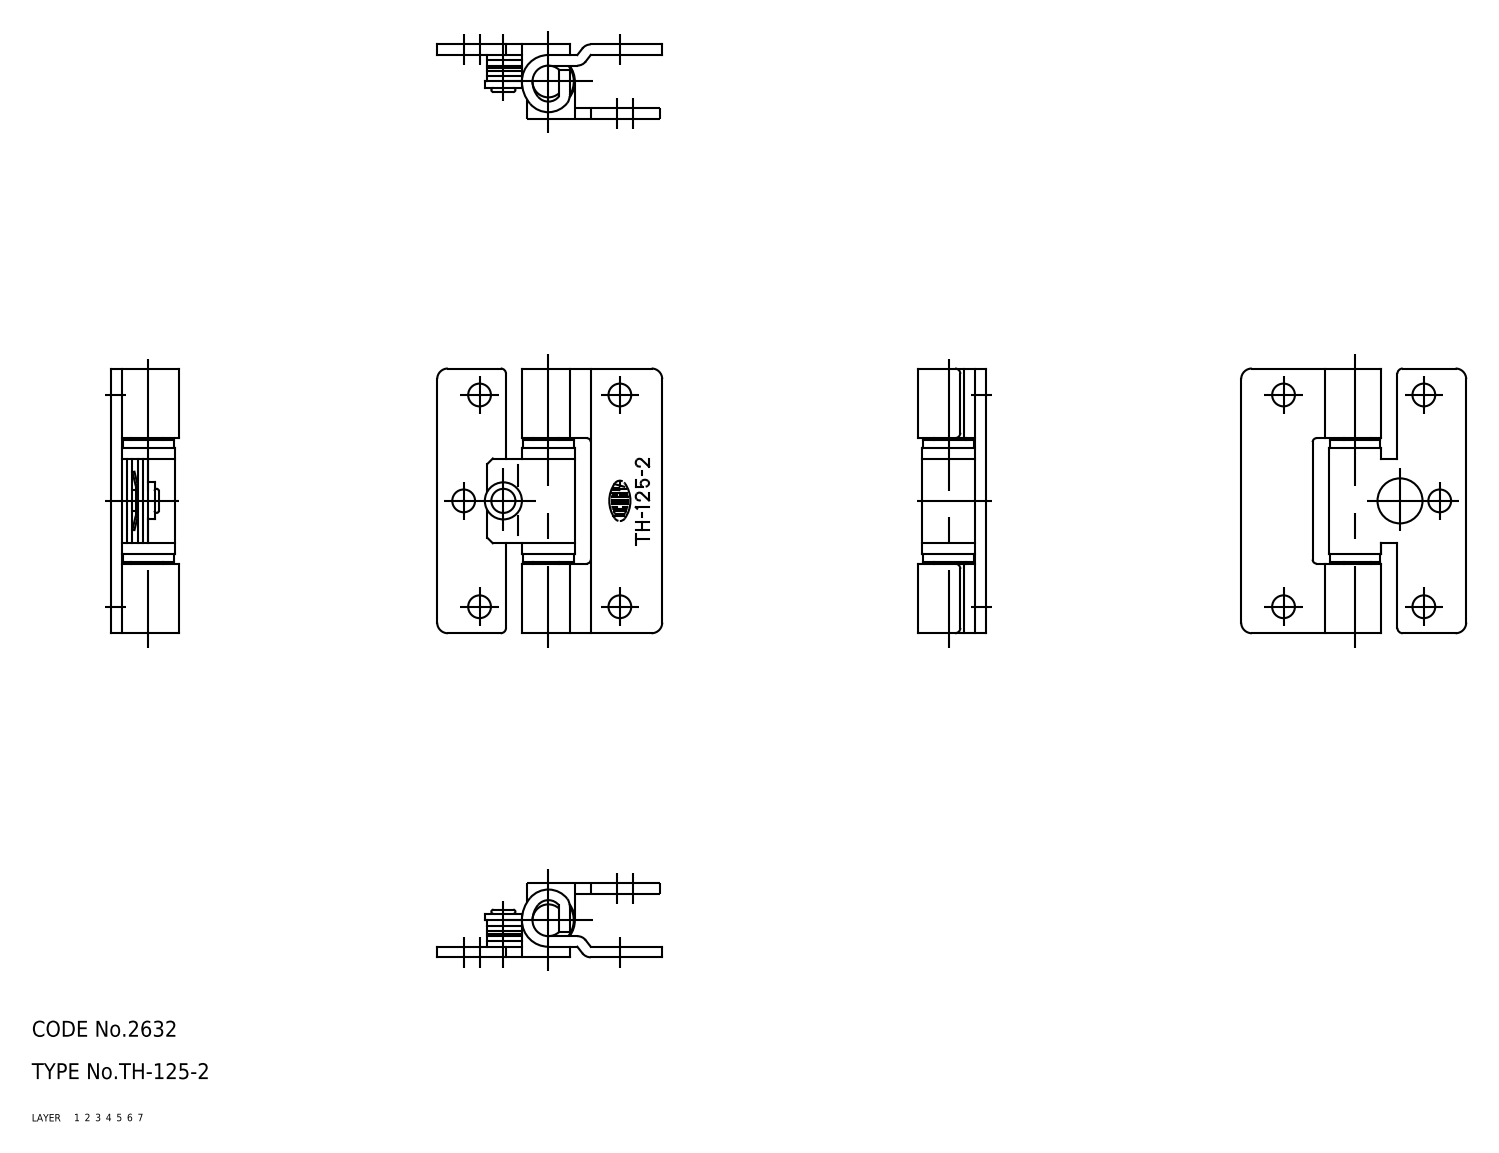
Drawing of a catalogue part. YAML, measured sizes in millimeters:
part_name: "washer_2; washer_1; spacer; shaft (+5 more)"
step_written_by: "CADfix (AUTOMOTIVE_DESIGN)"
units: millimeters
bodies: {solids: 10, faces: 168, planar: 0, cylindrical: 0, other: 168}
overall_size: [50, 42.5, 12.8]
volume: 7543
surface_area: 10281
